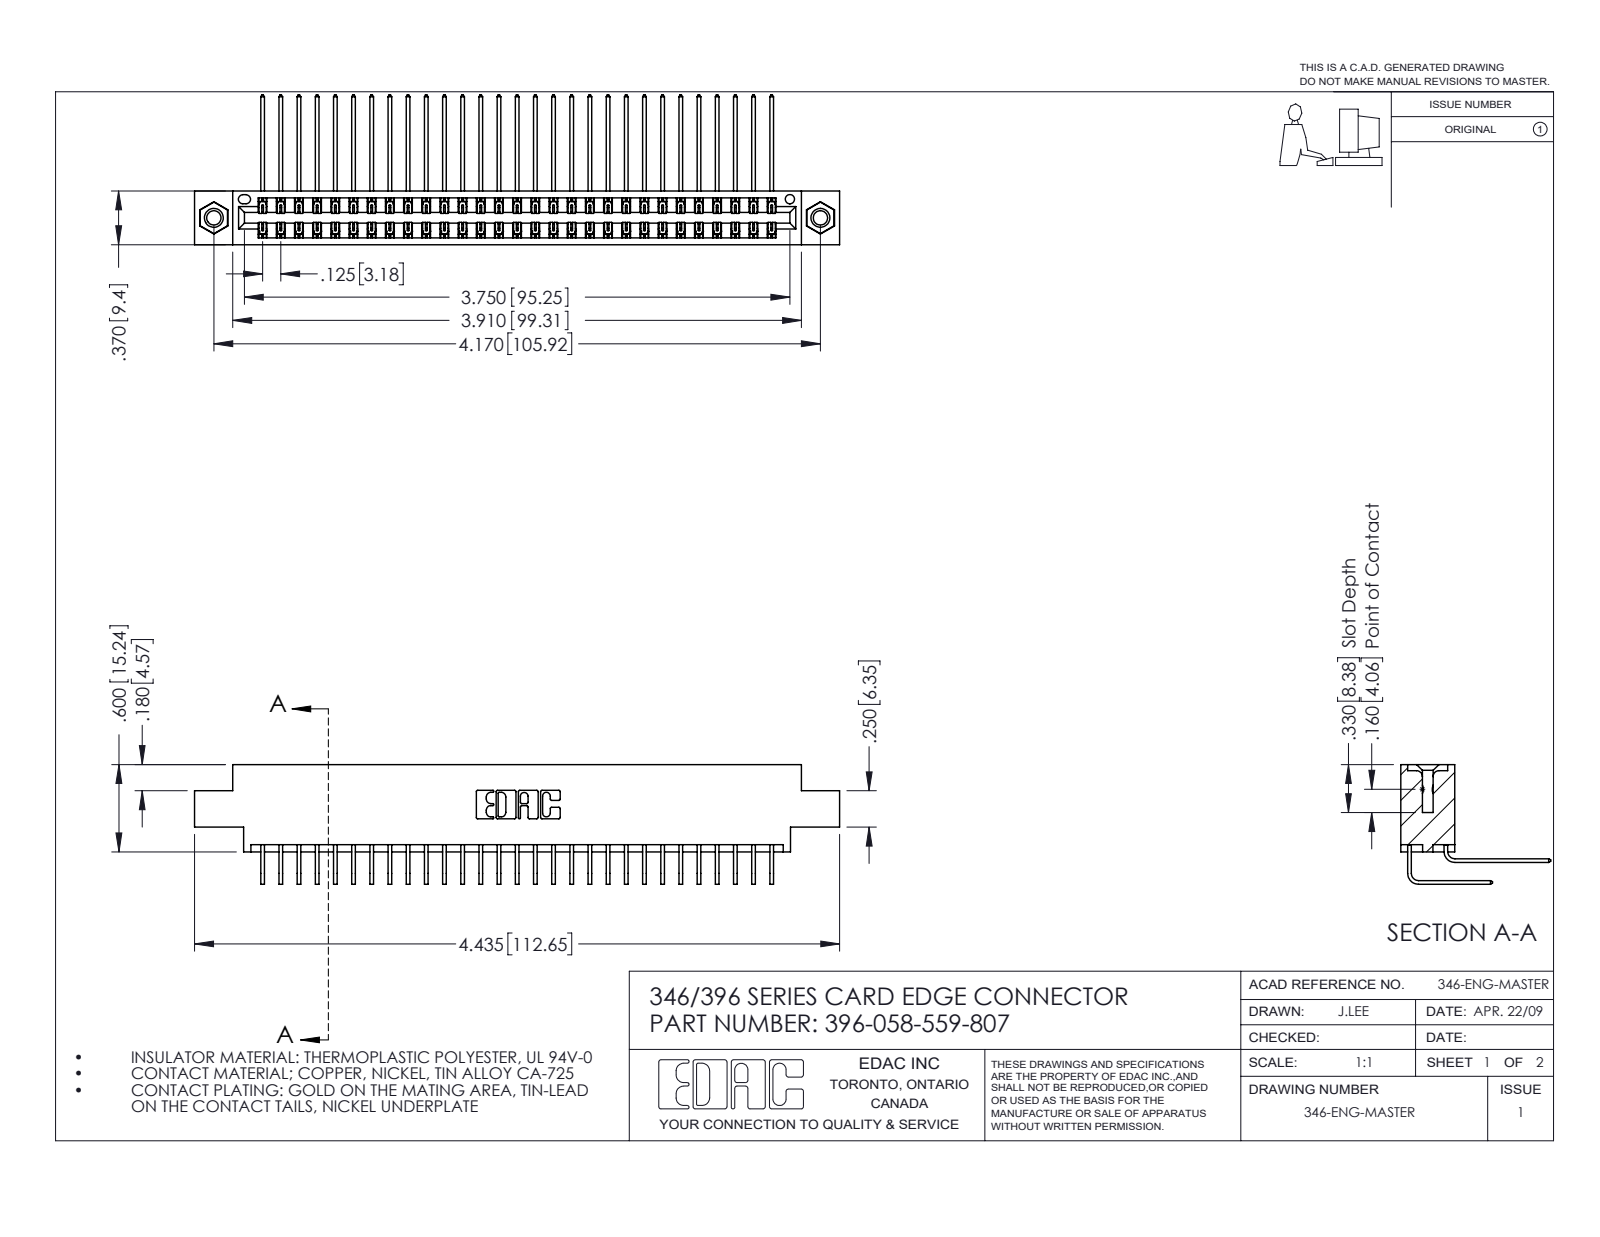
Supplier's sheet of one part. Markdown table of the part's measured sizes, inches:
| quantity | value |
| --- | --- |
| part name | 345-292-001_559 Tail - 2; 396-058-559-807; 345-292-001_558 559 Tail - 1; 346 Part_0.170 Offset - 0.156 Dia-TI (+1 more) |
| STEP written by | SolidWorks 2016 (CONFIG_CONTROL_DESIGN) |
| units | inches |
| bodies | 61 solids, 3318 faces (2258 planar, 1044 cylindrical, 16 other) |
| overall size | 4.435 × 1.03 × 0.823 |
| volume | 0.674 in³ |
| surface area | 26.05 in² |
| round holes (diameter × count) | 0.098 × 2, 0.125 × 2, 0.156 × 2, 0.064 × 1 |
| round bosses / shafts (diameter × count) | 0.155 × 2 |
| partial cylindrical surfaces (radius × count) | 0.006 × 87, 0.01 × 22, 0.007 × 6, 0.031 × 6, 0.026 × 3, 0.014 × 2, 0.022 × 2, 0.024 × 2 |
| main face-to-face distances | 0.048, 0.322, 0.025, 0.37, 0.25, 0.072, 0.298, 0.275, 0.222, 0.148 |
| hole center spacings | 0.246, 3.962, 4.17 |
